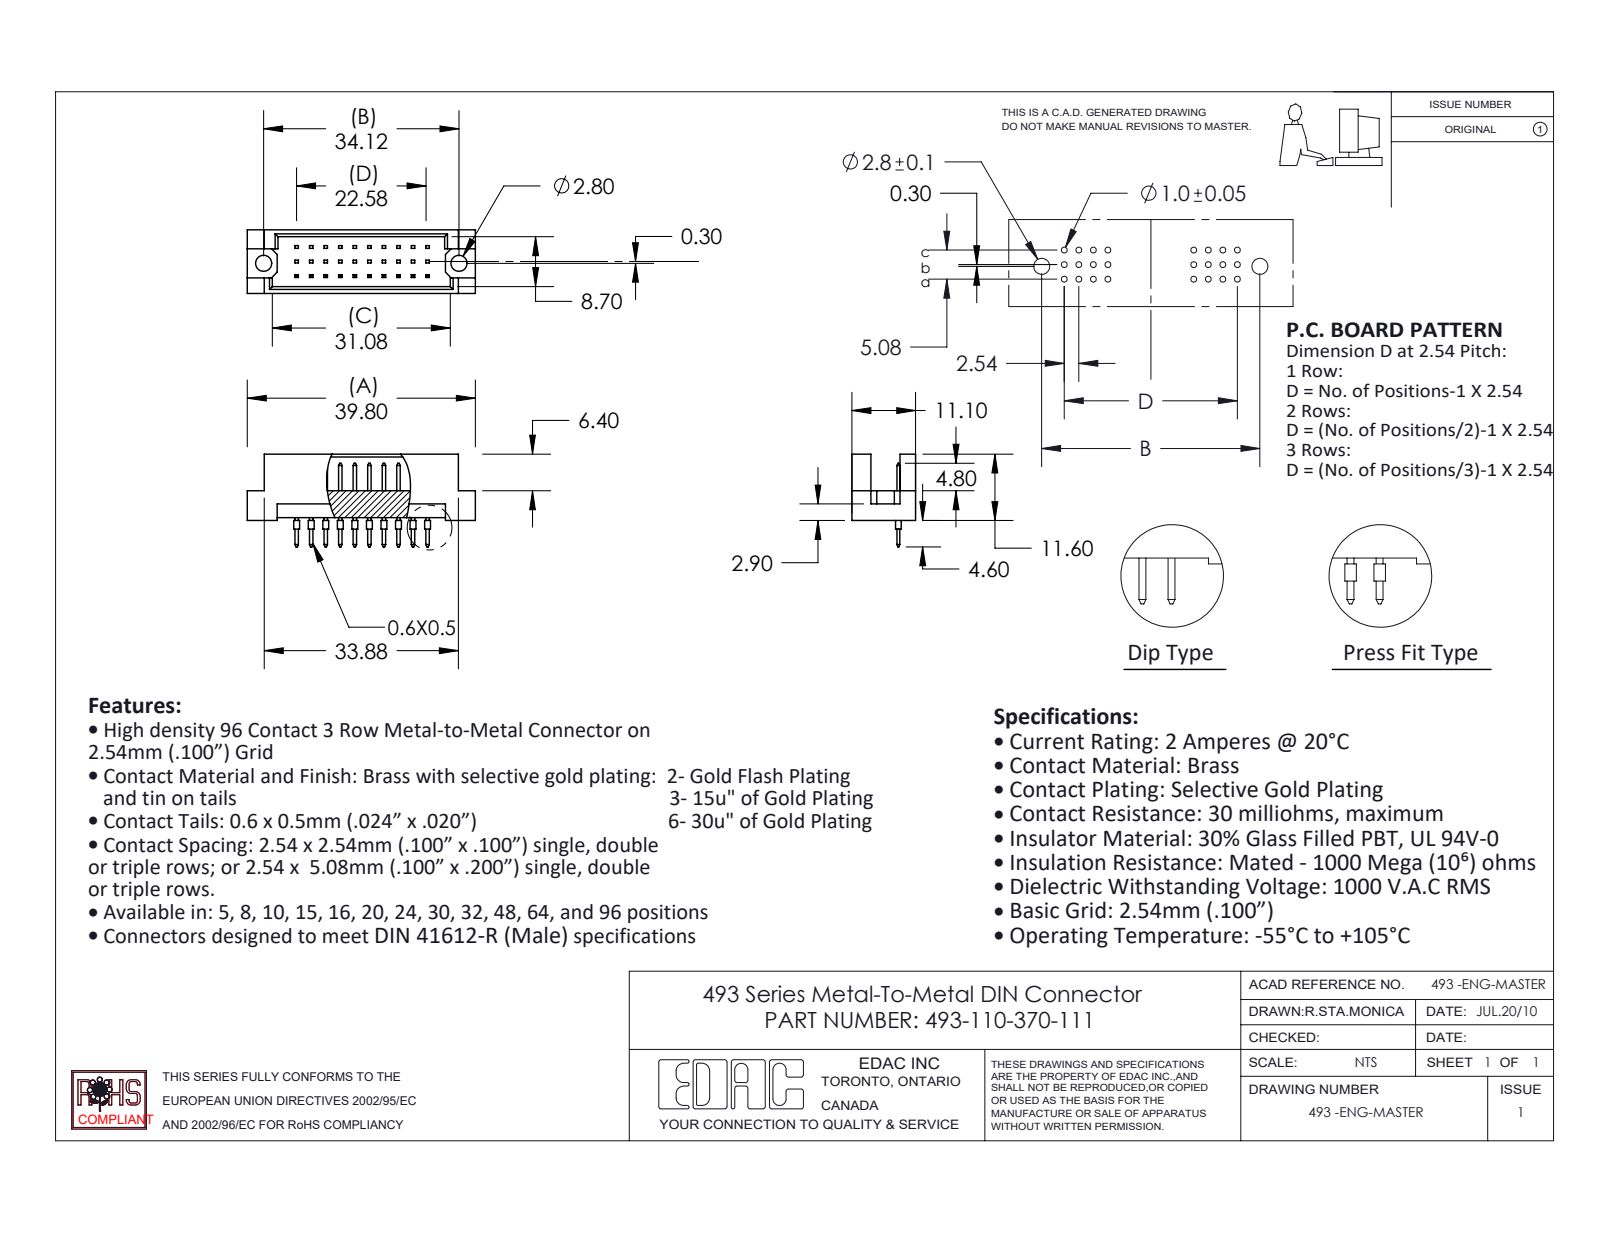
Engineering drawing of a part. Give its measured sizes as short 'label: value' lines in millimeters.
name: 493 Part_30; 493-110-370-111; 493-290_70
written by: SolidWorks 2020 (CONFIG_CONTROL_DESIGN)
unit: mm
bodies: 11 solids, 392 faces (368 planar, 24 cylindrical, 0 other)
size: 39.8 × 16.2 × 11.1
volume: 2 423 mm³; area: 3 079 mm²
holes: 2× ⌀2.8
bosses: 10× ⌀1
face distances: 1.2, 9.9, 11.1, 8.7, 2.54, 0.5, 4.7, 5.08, 2.76, 3.26
hole spacings: 34.12
